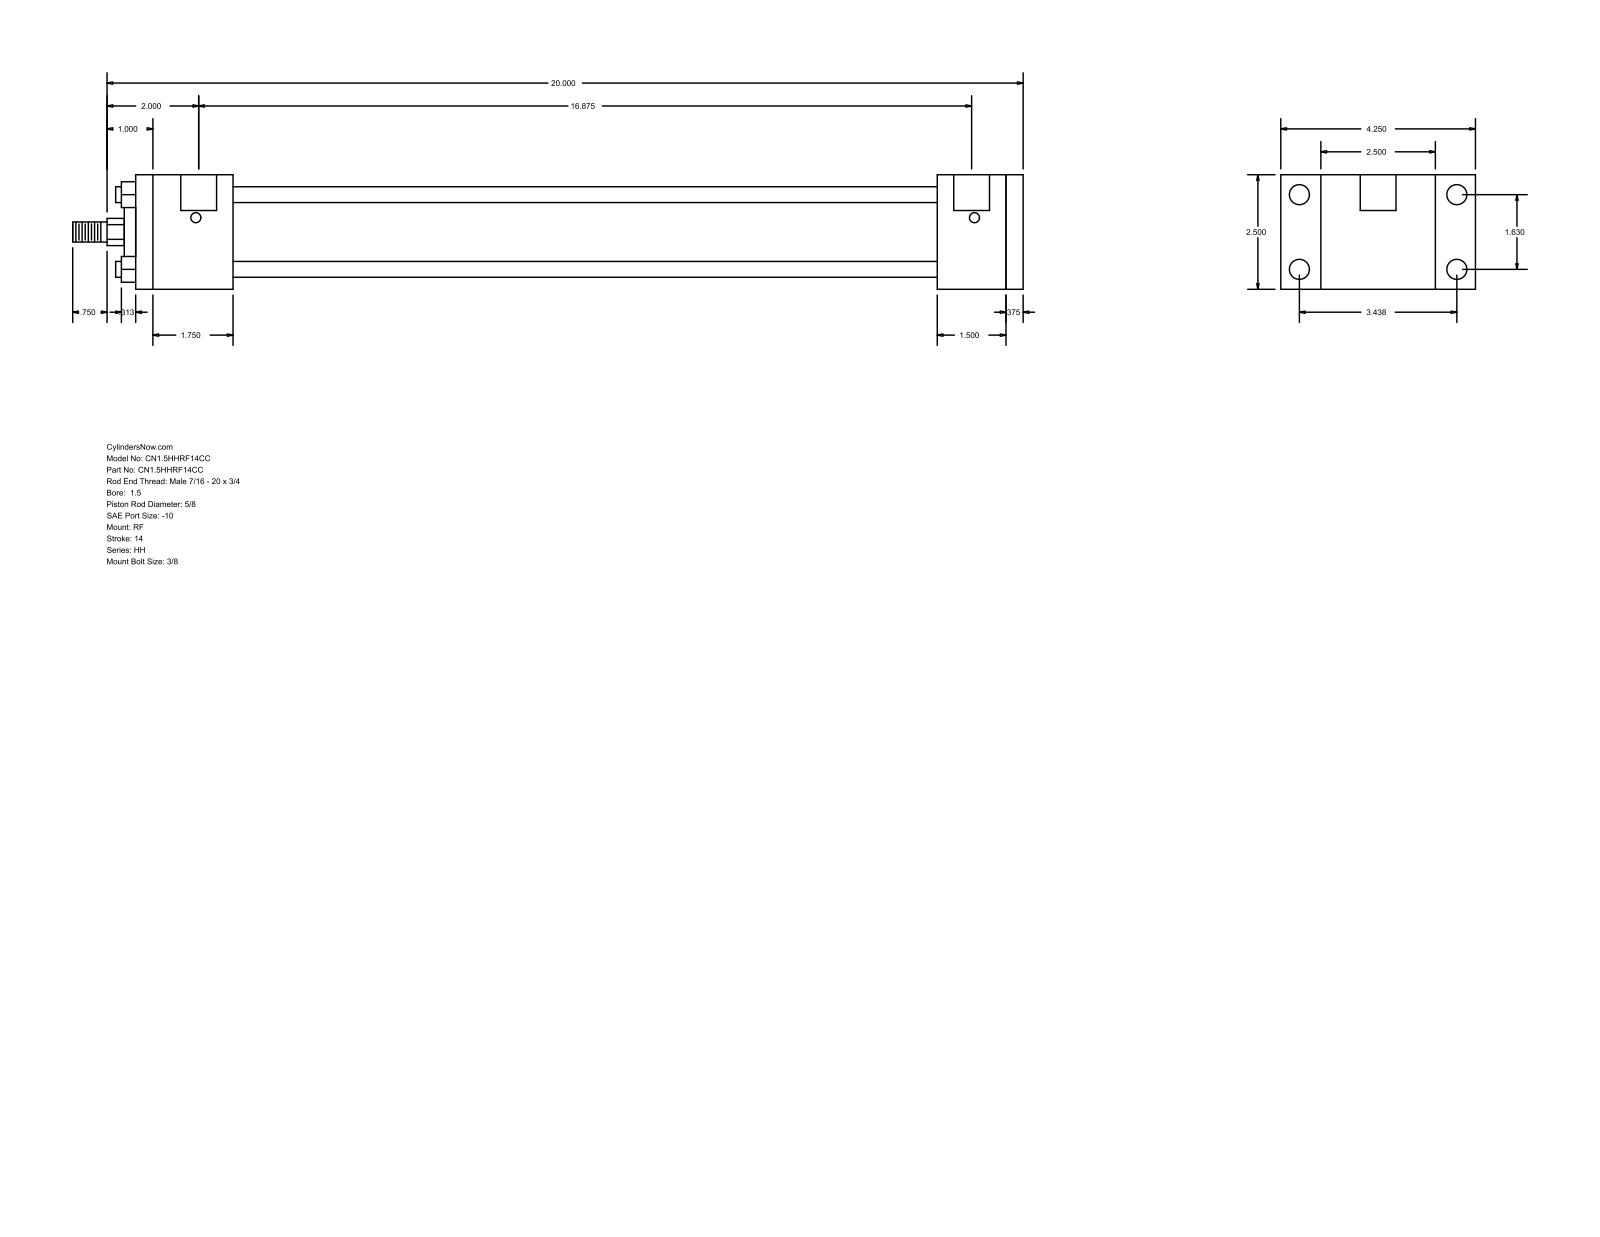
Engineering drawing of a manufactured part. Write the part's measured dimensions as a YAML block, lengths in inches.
part_name: "HH_RF__0150_0.625"
step_written_by: "GSSL Pune (CONFIG_CONTROL_DESIGN)"
units: inches
bodies: {solids: 0, faces: 92, planar: 64, cylindrical: 28, other: 0}
overall_size: [20.75, 4.25, 2.5]
round_holes:
  - {diameter: 0.219, count: 4}
  - {diameter: 0.438, count: 4}
  - {diameter: 0.781, count: 2}
round_bosses_or_shafts:
  - {diameter: 0.345, count: 4}
  - {diameter: 1.75, count: 1}
  - {diameter: 1.125, count: 1}
  - {diameter: 0.625, count: 1}
  - {diameter: 0.437, count: 1}
partial_cylinders:
  - {radius: 0.297, count: 1}
face_to_face_distances: [2.5, 19.375, 1.5, 19, 0.375, 2.125, 17.5, 15.375, 16.875, 17.25]
hole_center_spacings: [1.63, 3.438, 3.805, 17, 0.062, 0.063, 16.875, 16.937]
